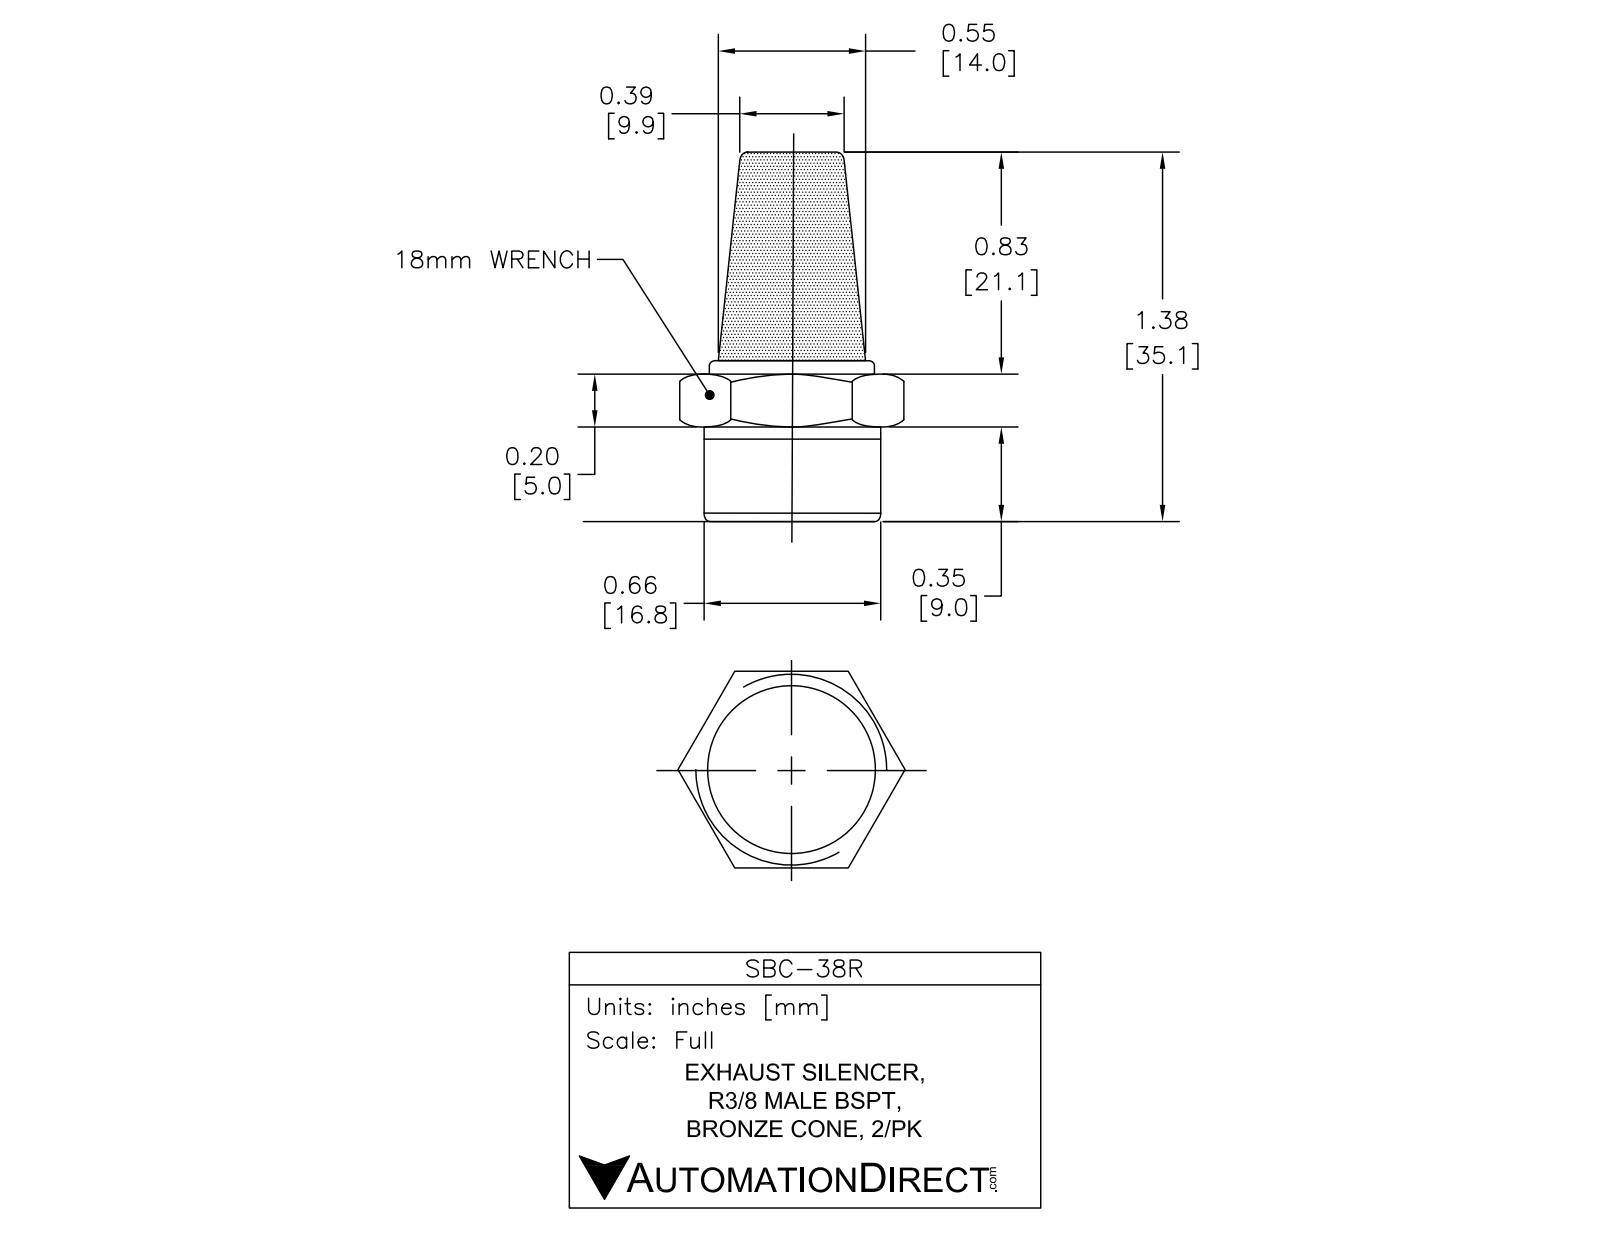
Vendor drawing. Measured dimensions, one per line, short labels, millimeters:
name: SBC-38R
written by: SolidWorks 2015 (CONFIG_CONTROL_DESIGN)
unit: mm
bodies: 1 solid, 56 faces (13 planar, 17 cylindrical, 26 other)
size: 35.7 × 18 × 15.6
volume: 3 100 mm³; area: 2 923 mm²
holes: 1× ⌀8
bosses: 1× ⌀14.7
face distances: 15.6, 35.7, 32.2, 3.6, 13.7, 18.4, 22, 8.1, 5.6, 24
